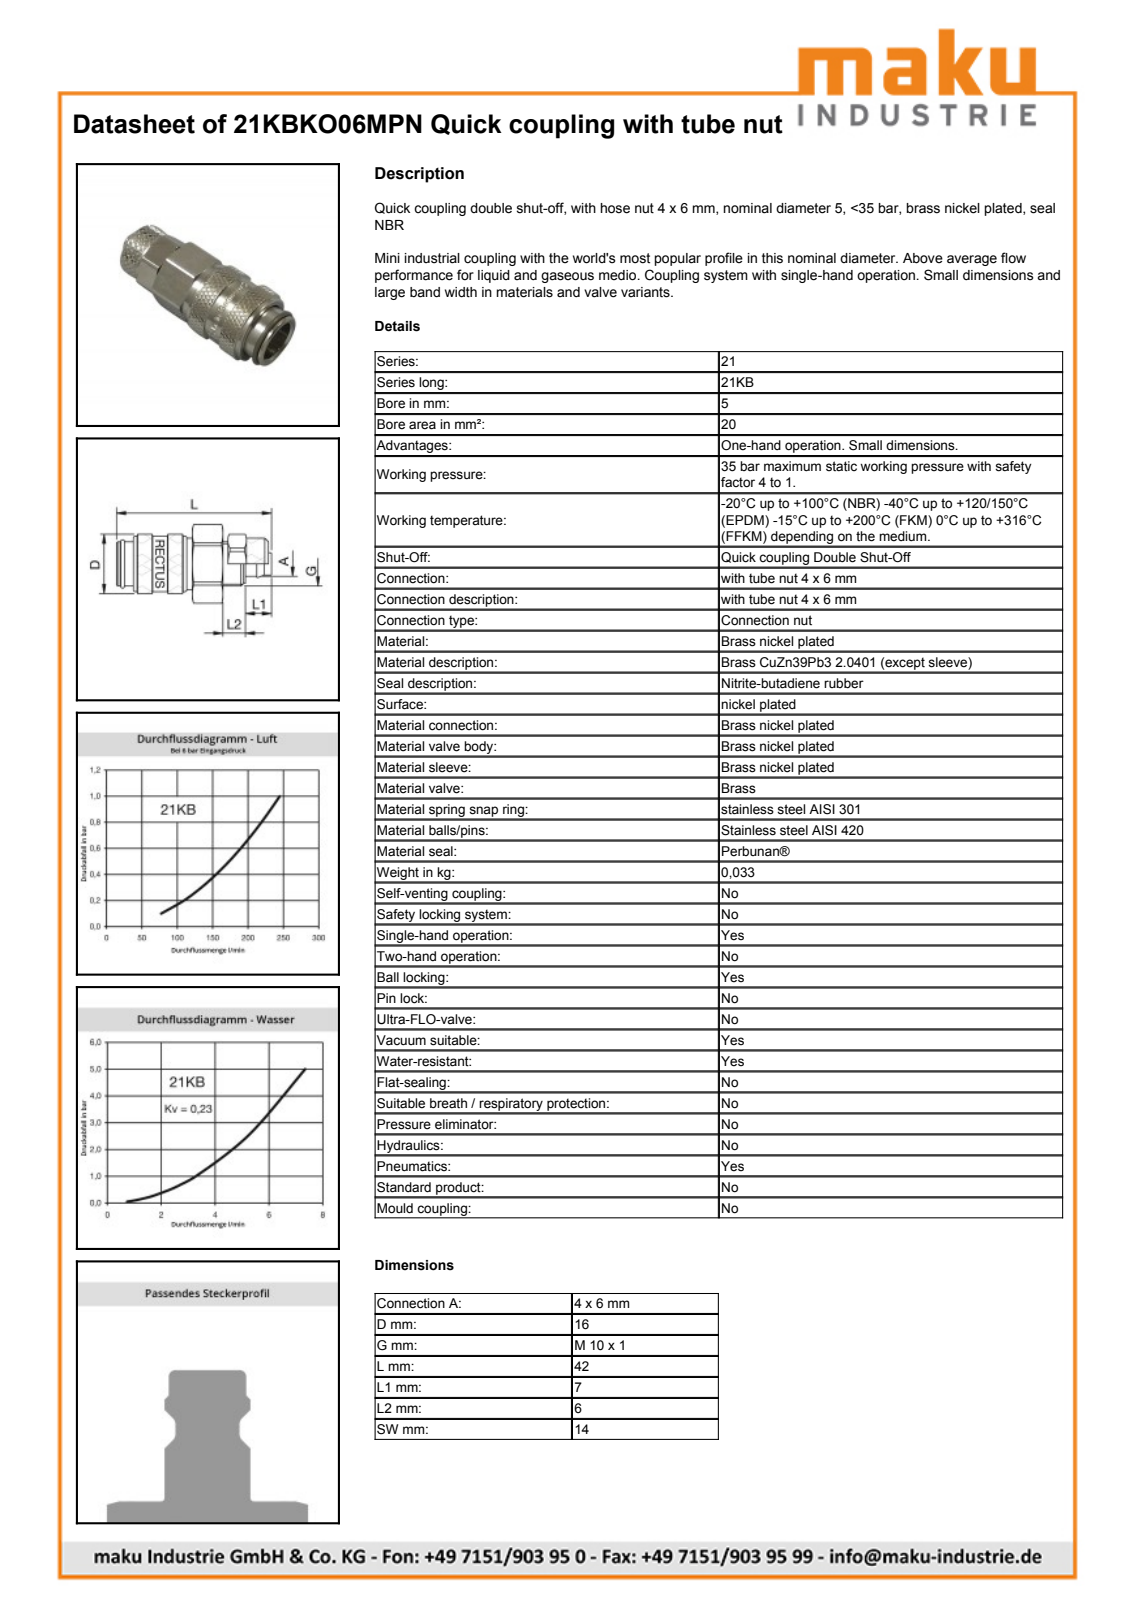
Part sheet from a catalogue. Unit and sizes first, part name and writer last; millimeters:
Units: millimetres
Overall size (bounding box): 42 × 16.15 × 16.15
Round holes (diameter × count): ⌀6.2 ×1, ⌀8.2 ×1, ⌀9 ×1, ⌀10 ×1, ⌀10.4 ×1, ⌀10.45 ×1, ⌀10.5 ×1, ⌀10.7 ×1, ⌀12.15 ×1, ⌀14 ×1
Round bosses / shafts (diameter × count): ⌀16.15 ×1, ⌀15.1 ×1, ⌀12 ×1, ⌀11.4 ×1, ⌀11.15 ×1, ⌀8.4 ×1, ⌀4.6 ×1, ⌀4 ×1
Partial cylindrical surfaces — rounded edges, fillets, slot ends (radius × count): R6.7 ×1, R7.45 ×1, R7.9 ×1
Main face-to-face distances: 14, 12, 13.85, 28.9, 1.75, 27.15, 6, 11, 36.4, 5
Volume: 4 700 mm³ · Surface area: 5 523 mm²
Bodies: 2 solids, 455 faces (176 planar, 76 cylindrical, 203 other)
Part name (STEP PRODUCT): D111164
STEP written by: Autodesk Inventor 2013 (AUTOMOTIVE_DESIGN)
